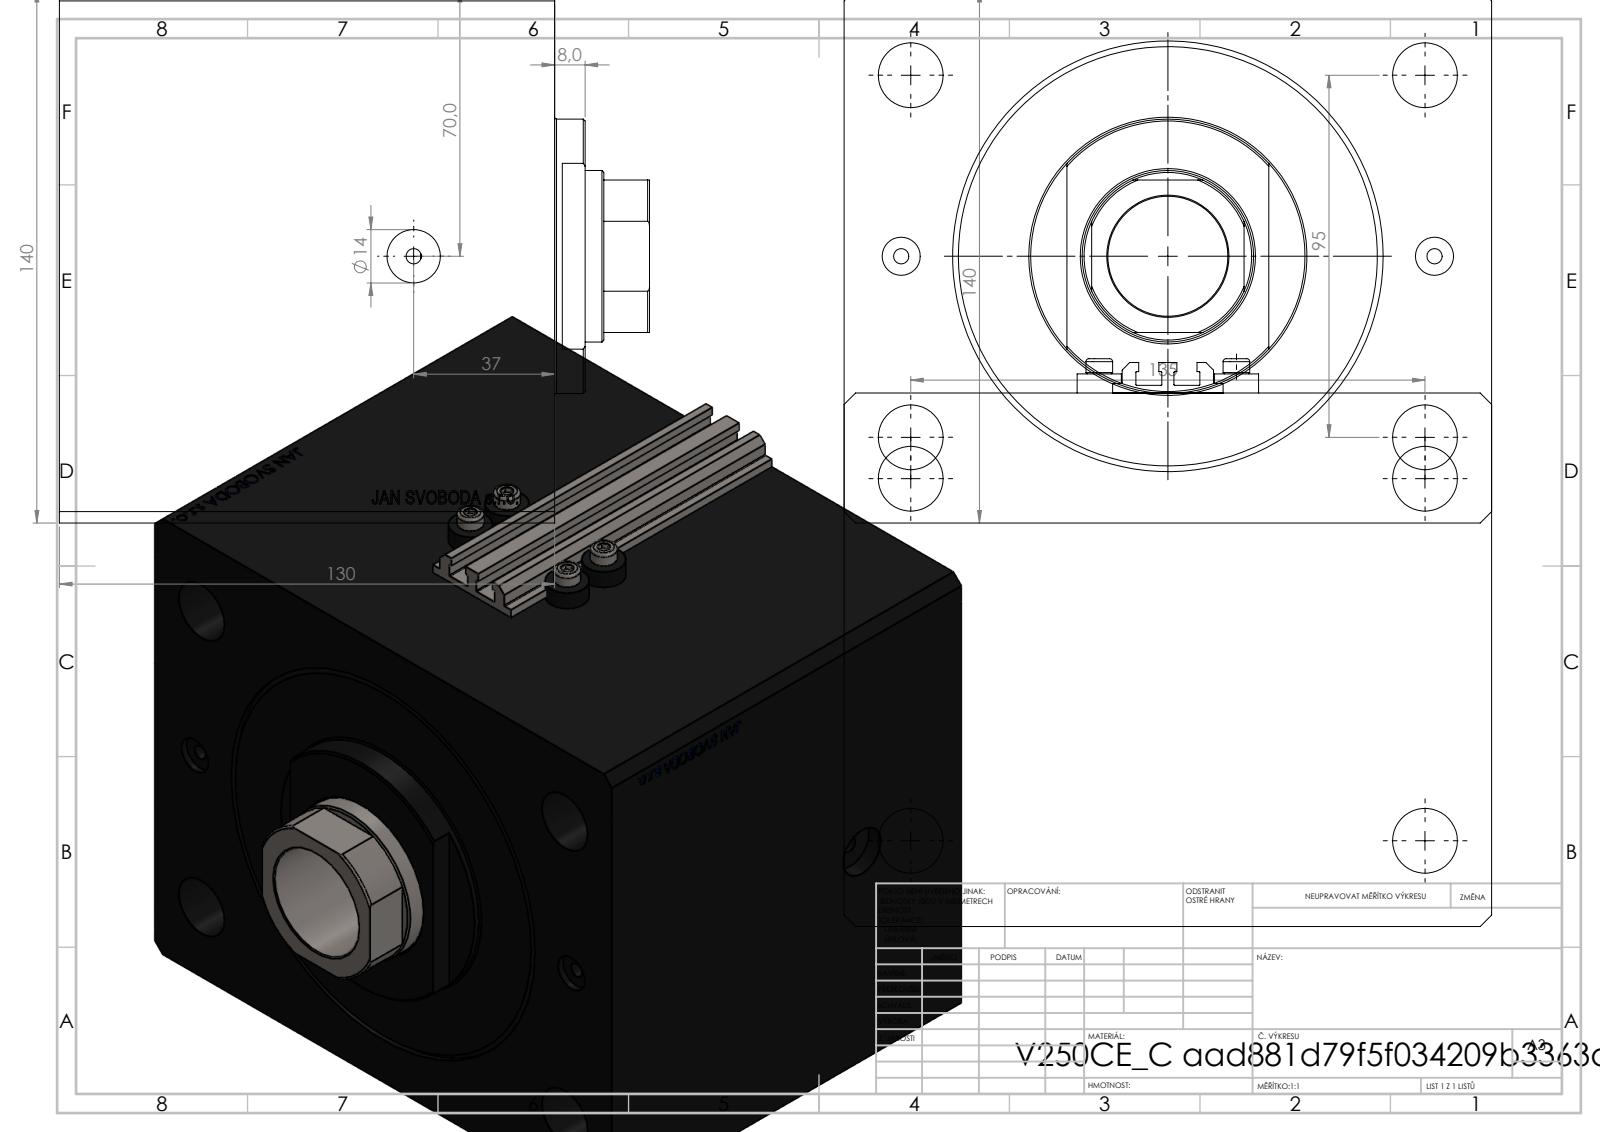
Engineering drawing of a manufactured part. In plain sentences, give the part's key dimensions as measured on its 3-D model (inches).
The part is named "V250CE_C_Body; ALLEN BOLT V250CE; V250CE_VC_C; V250CE_C_VCP". Its 3-D file was written by "SolidWorks 2019 (CONFIG_CONTROL_DESIGN)". It is 8 solids with 1034 faces: 504 planar, 86 cylindrical and 444 other. Overall it measures 6.693 by 6.098 by 5.866 inches. Its volume is 175 cubic inches and its surface area 441.5 square inches. Round holes: 8 of diameter 0.157, 4 of diameter 0.669, 2 of diameter 0.394, 2 of diameter 0.551, 1 of diameter 1.24, 1 of diameter 1.772, 1 of diameter 3.937, 1 of diameter 4.449. Round bosses or shafts: 4 of diameter 0.457, 4 of diameter 0.276, 1 of diameter 2.835. Partial cylindrical surfaces (rounded edges, fillets, slot ends): 10 of radius 0.008, 1 of radius 0.866. The main face-to-face distances are 5.512, 5.118, 6.693, 1.138, 3.98, 2.598, 3.736, 1.382, 2.949, 1.811. The hole center spacings are 1.873, 3.25, 5.727, 0.535, 1.417, 1.515, 2.756, 3.74.
